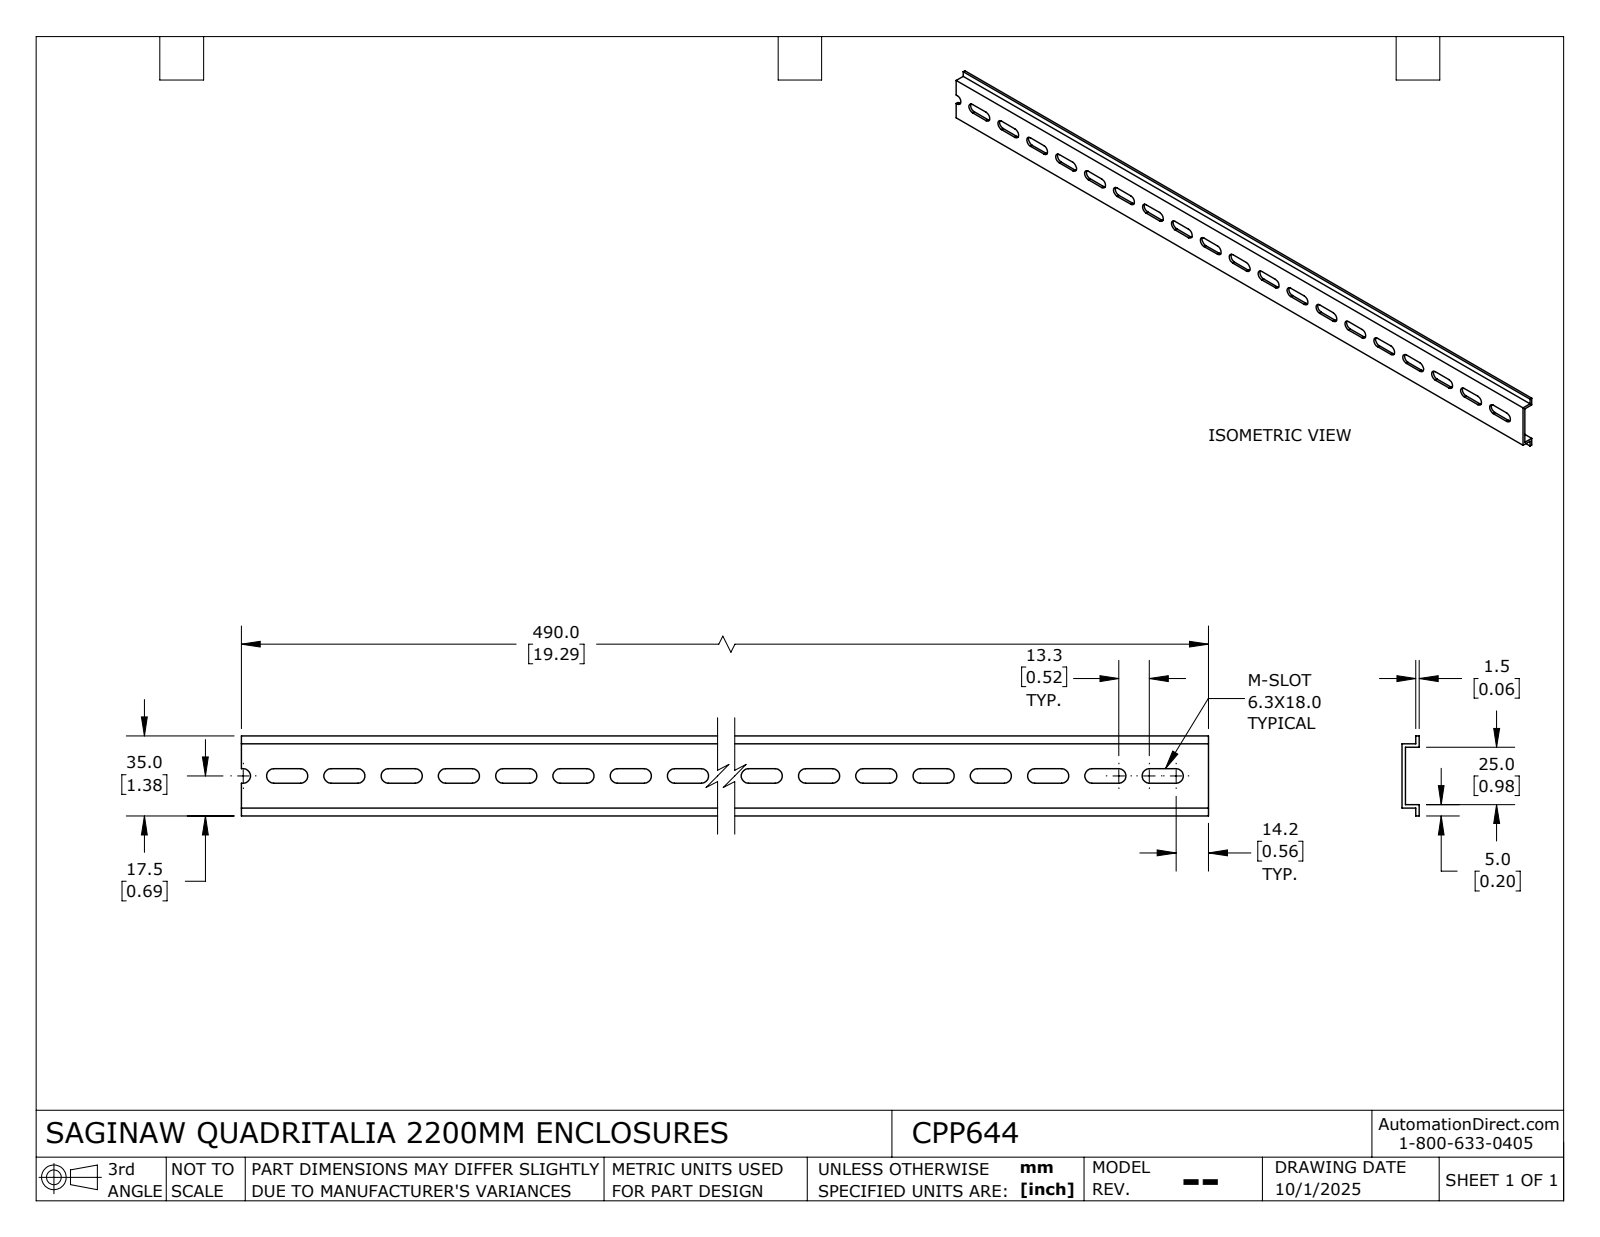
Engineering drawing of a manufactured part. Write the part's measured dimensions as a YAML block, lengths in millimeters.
part_name: "CPP644_Default"
step_written_by: "SolidWorks 2024 (CONFIG_CONTROL_DESIGN)"
units: millimeters
bodies: {solids: 1, faces: 94, planar: 55, cylindrical: 39, other: 0}
overall_size: [490, 35, 7.5]
volume: 31524
surface_area: 44882
partial_cylinders:
  - {radius: 3.15, count: 39}
face_to_face_distances: [1.5, 6, 26.5, 7.5, 4.5, 28, 25, 3.5, 5, 30]
